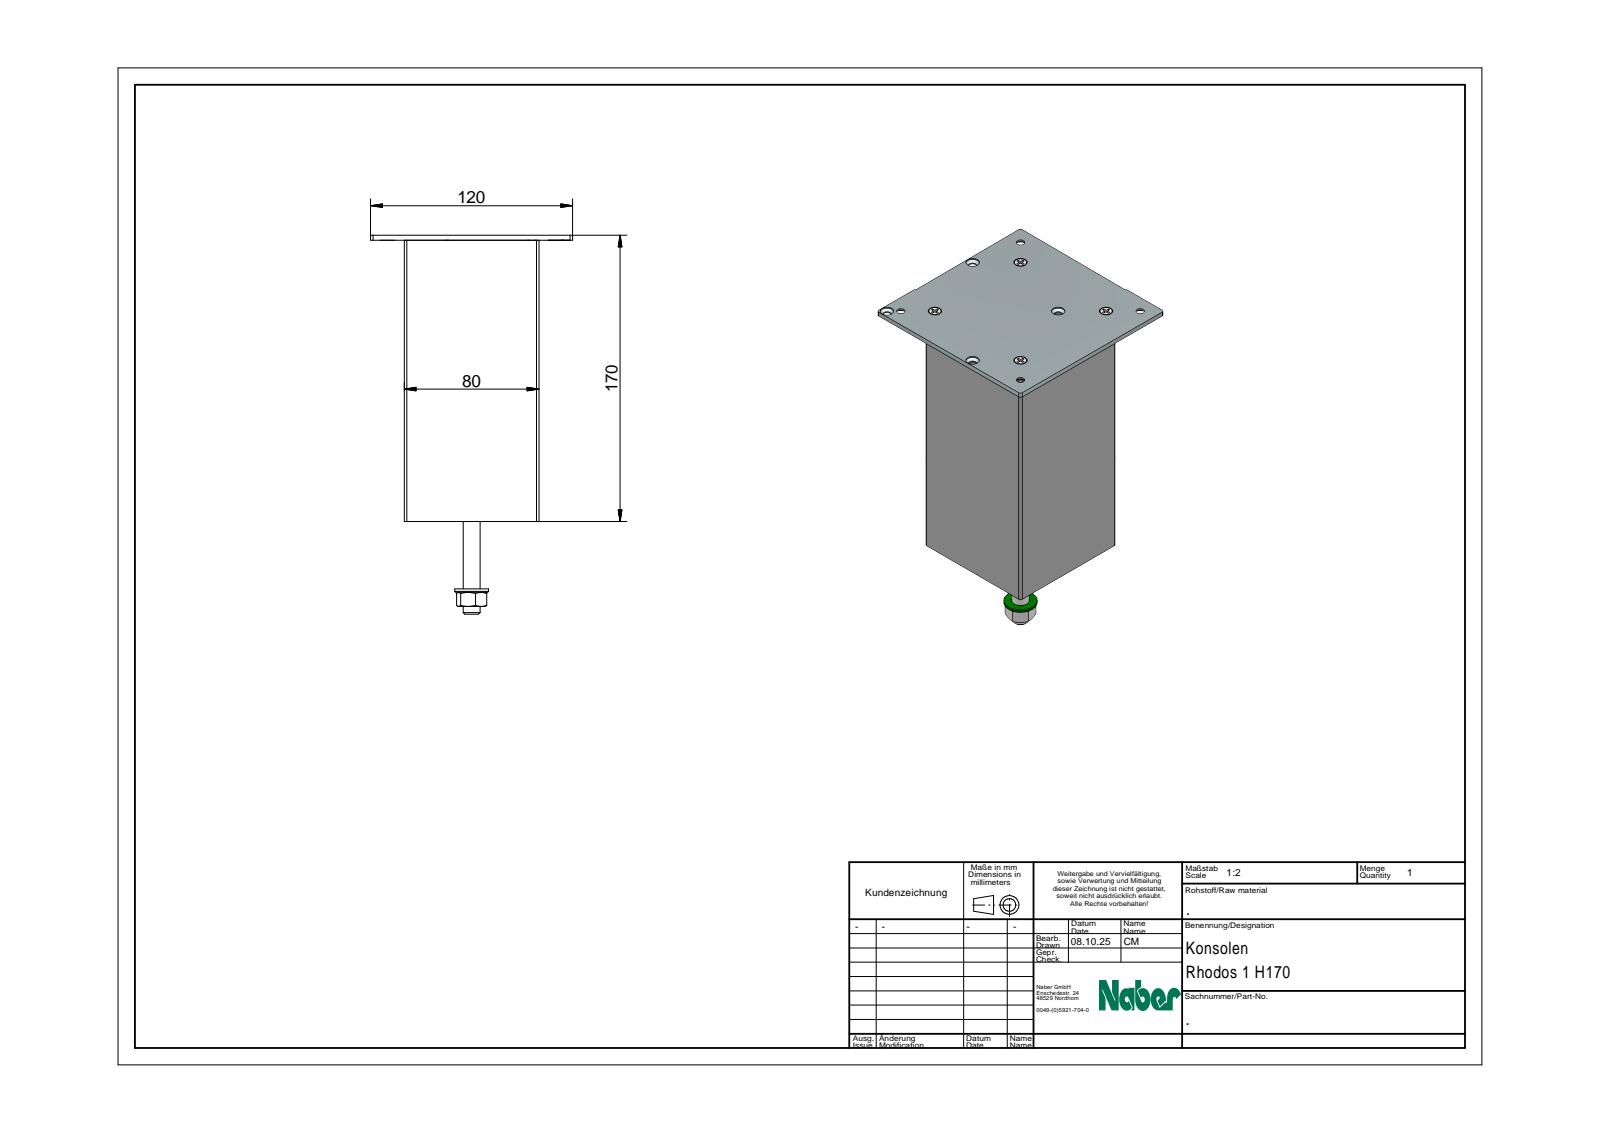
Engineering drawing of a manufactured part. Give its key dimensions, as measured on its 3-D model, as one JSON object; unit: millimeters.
{"part_name": "Barkonsole Jumbo-170|Profil Jumbo 167mm#Profil Jumbo 167mm;Profil Jumbo 167mm", "step_written_by": "Spatial InterOp 3D (AUTOMOTIVE_DESIGN)", "units": "millimeters", "bodies": {"solids": 14, "faces": 483, "planar": 145, "cylindrical": 200, "other": 138}, "overall_size": [225, 120, 120], "volume_mm3": 178443, "surface_area_mm2": 157029, "round_holes": [[5, 12], [8, 8], [6.65, 2], [8.38, 1], [10.11, 1], [10.5, 1]], "round_bosses_or_shafts": [[4, 4], [2.8, 4], [2, 4], [10, 3], [8, 2], [38, 1], [20, 1]], "partial_cylinders_radius": [[0.75, 16], [0.15, 8], [1.5, 8], [1.75, 4], [3.75, 4]], "face_to_face_distances": [1.8, 78.2, 80, 76.4, 3, 20, 21.8, 98.2, 100, 10], "hole_center_spacings": [71.5, 86.93, 20.15, 28.28, 50.56, 55.25, 70.71, 93.66]}
